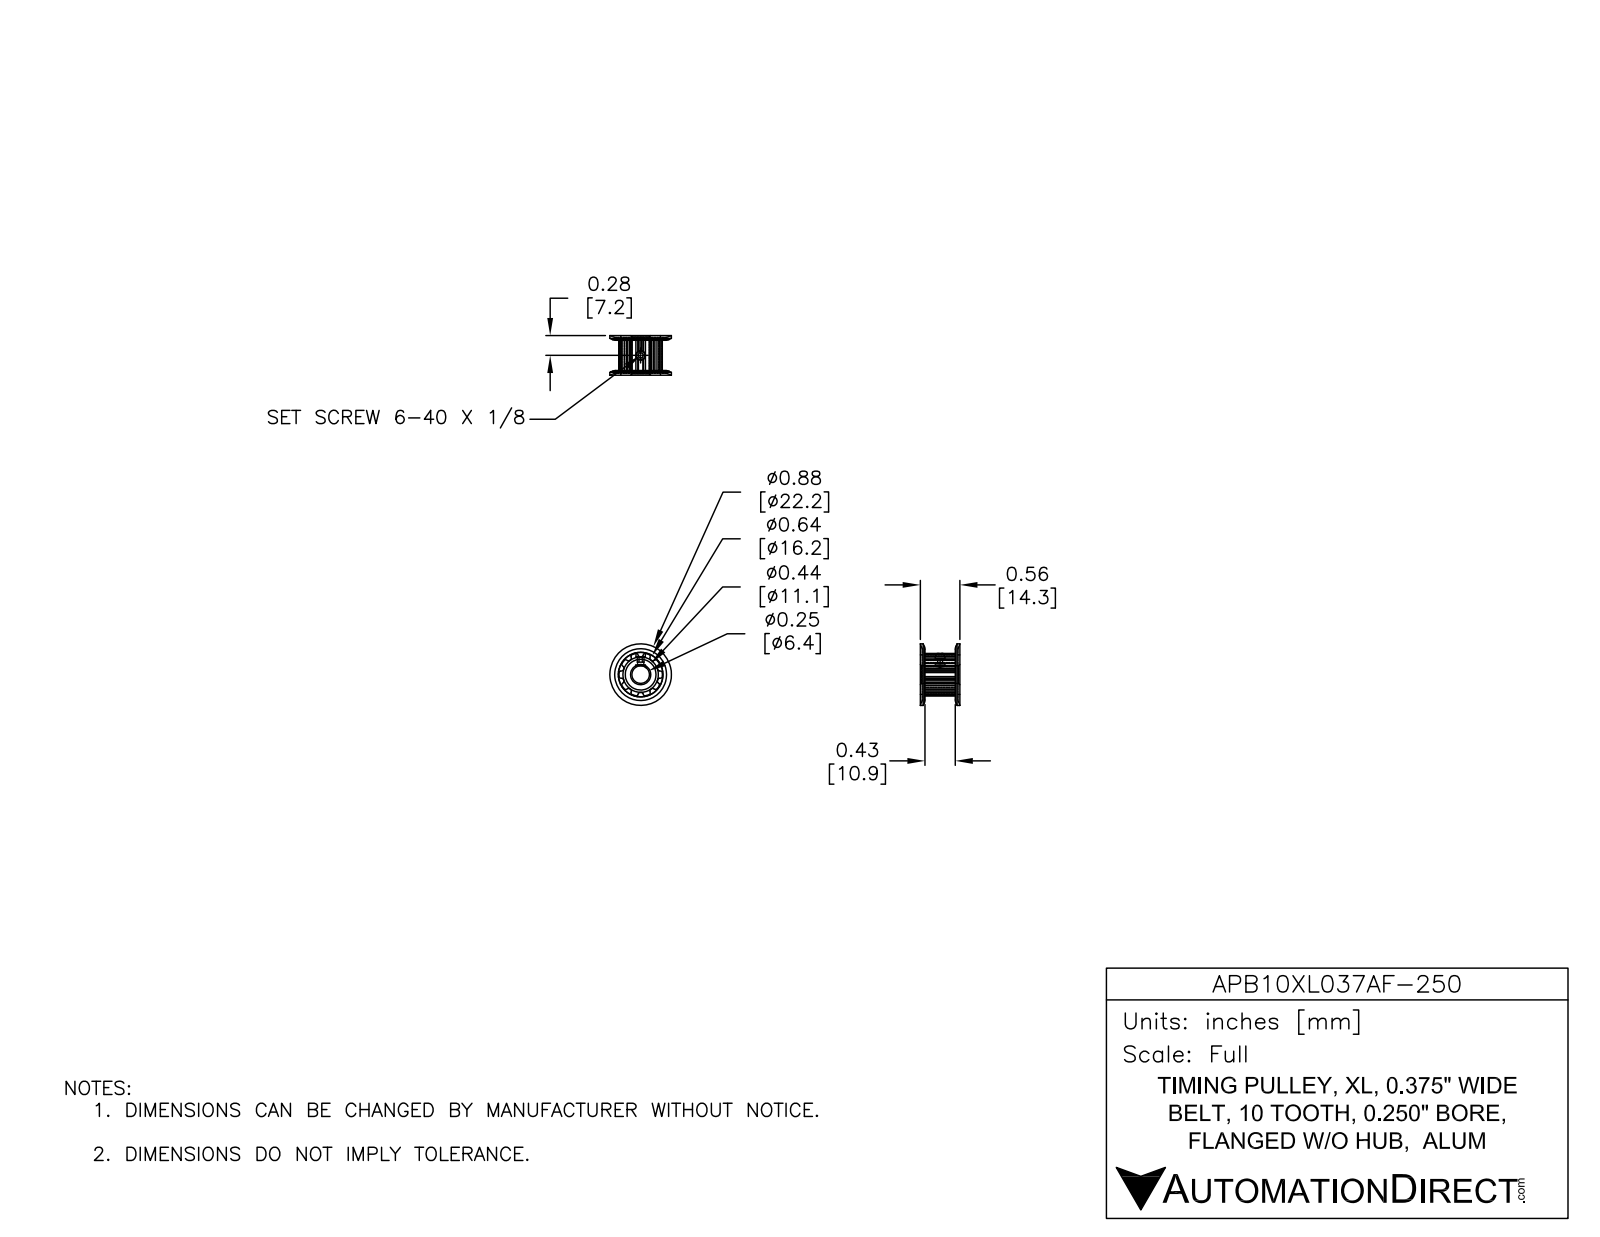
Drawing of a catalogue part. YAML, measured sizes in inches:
part_name: "APB10XL037AF-250"
step_written_by: "SolidWorks 2014 (AUTOMOTIVE_DESIGN)"
units: inches
bodies: {solids: 1, faces: 141, planar: 44, cylindrical: 77, other: 20}
overall_size: [0.875, 0.875, 0.563]
volume: 0.132
surface_area: 3.639
round_holes:
  - {diameter: 0.088, count: 2}
  - {diameter: 0.25, count: 1}
round_bosses_or_shafts:
  - {diameter: 0.496, count: 1}
partial_cylinders:
  - {radius: 0.015, count: 37}
  - {radius: 0.008, count: 2}
  - {radius: 0.062, count: 1}
  - {radius: 0.063, count: 1}
  - {radius: 0.254, count: 1}
face_to_face_distances: [0.031, 0.5, 0.531, 0.166, 0.617, 0.563, 0.063, 0.469, 0.437]
